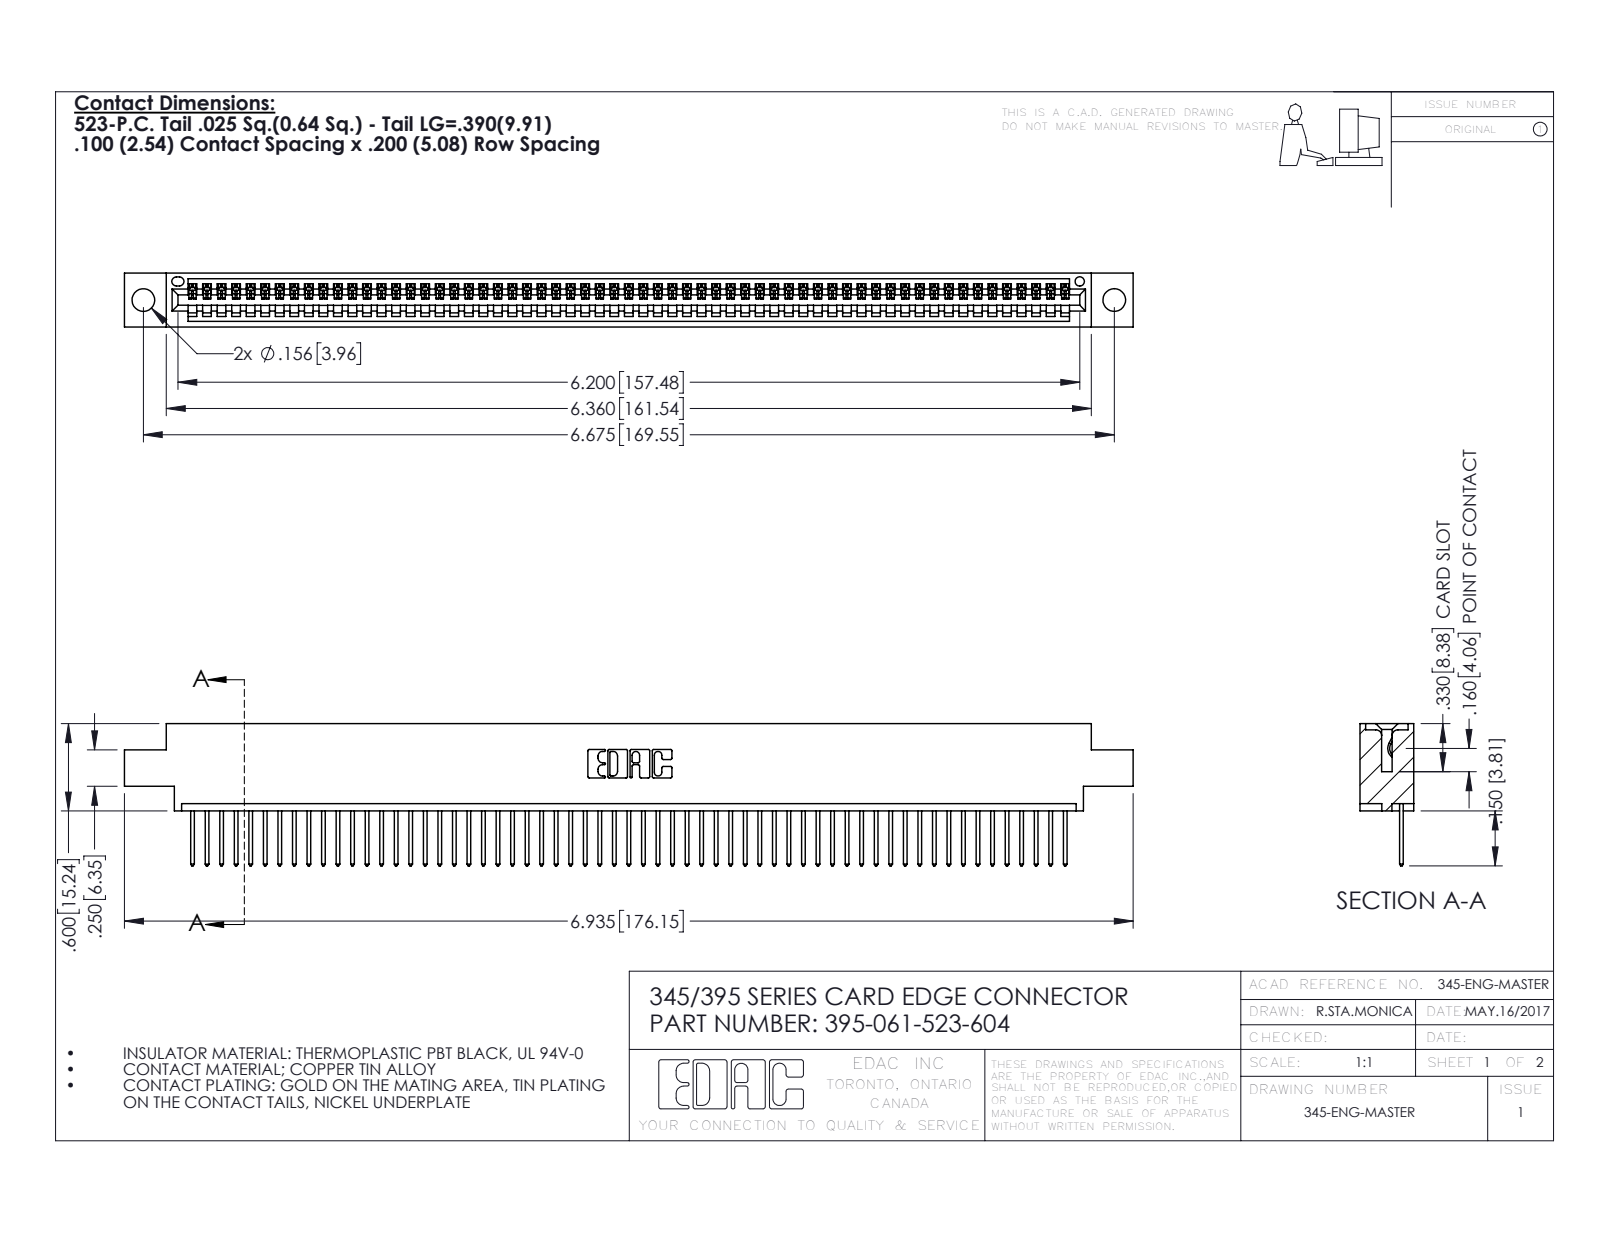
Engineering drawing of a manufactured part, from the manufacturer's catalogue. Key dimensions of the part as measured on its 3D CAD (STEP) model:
Part name (STEP PRODUCT): 395-061-523-604; 345-292-001_345-293-123; 345 Part_0.170 Offset - 0.156 Dia-TH
STEP written by: SolidWorks 2016 (CONFIG_CONTROL_DESIGN)
Units: inches
Bodies: 62 solids, 3668 faces (2524 planar, 1144 cylindrical, 0 other)
Overall size (bounding box): 6.935 × 0.977 × 0.37
Volume: 1.017 in³ · Surface area: 34.72 in²
Round holes (diameter × count): ⌀0.156 ×2, ⌀0.064 ×1
Partial cylindrical surfaces — rounded edges, fillets, slot ends (radius × count): R0.006 ×122, R0.01 ×122, R0.01 ×22, R0.007 ×6, R0.031 ×6, R0.026 ×3, R0.031 ×2, R0.04 ×2
Main face-to-face distances: 0.298, 0.072, 0.37, 0.098, 0.272, 0.025, 0.2, 0.225, 0.175, 0.149
Hole centre spacings: 0.27, 6.439, 6.675
